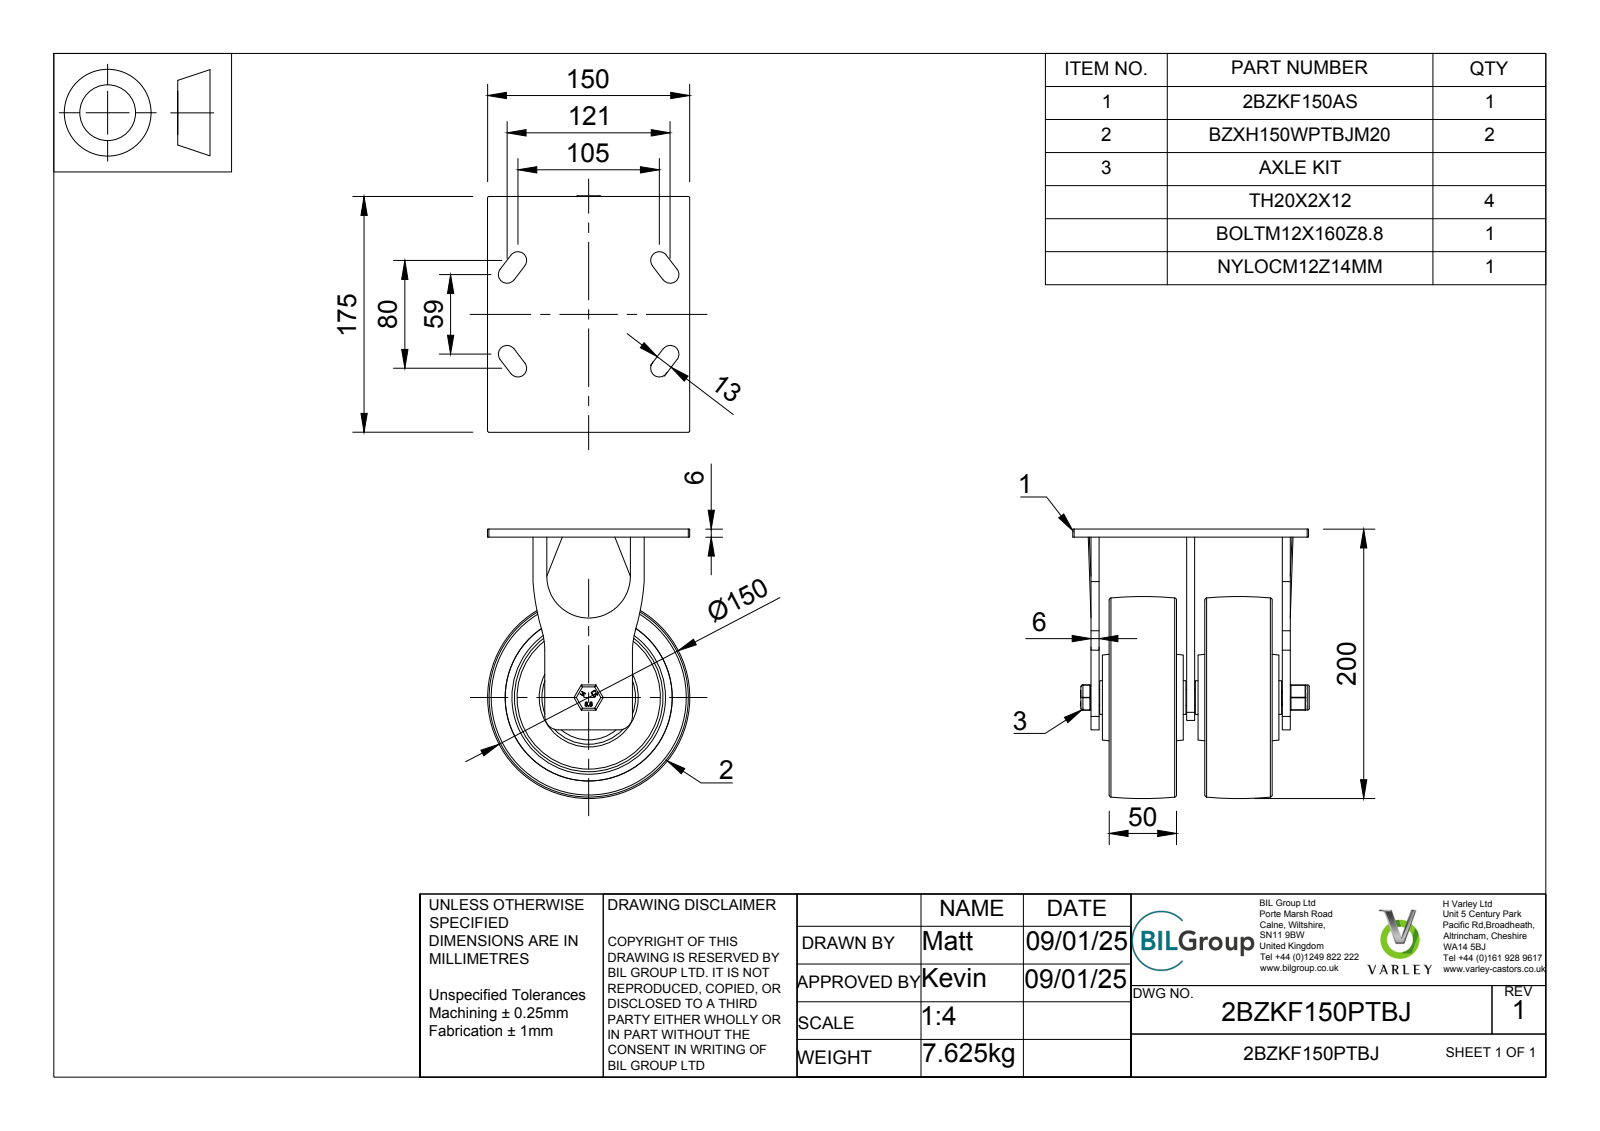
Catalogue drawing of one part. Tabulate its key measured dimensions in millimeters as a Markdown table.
| quantity | value |
| --- | --- |
| part name | 2BZKF150PTBJ v3; 2BZKF150AS v1; 2BZKF150AS; STEEL FABRICATED BRACKET (+8 more) |
| STEP written by | Autodesk Translation Framework v13.20.0.188 (AP242_MANAGED_MODEL_BASED_3D_ENGINEERING_MIM_LF) |
| units | millimeters |
| bodies | 66 solids, 2298 faces (1050 planar, 450 cylindrical, 798 other) |
| overall size | 200 × 175.5 × 150 |
| volume | 1 490 000 mm³ |
| surface area | 462 744 mm² |
| round holes (diameter × count) | 12 × 1, 12.2 × 1, 13 × 1, 14 × 1, 20 × 1, 28.5 × 1, 41.5 × 1, 42 × 1, 44 × 1, 47 × 1, 124 × 1 |
| round bosses / shafts (diameter × count) | 40.5 × 1, 40 × 1, 29 × 1, 27 × 1, 25 × 1, 24 × 1, 19.8 × 1, 18.5 × 1 |
| partial cylindrical surfaces (radius × count) | 6 × 26, 4 × 24, 0.5 × 18, 0.25 × 12, 6.5 × 8, 1.5 × 6, 0.47 × 4, 0.9 × 4 |
| main face-to-face distances | 71, 6, 35.5, 7.5, 57.5, 13.5, 63.5, 41.5, 106.5, 29.5 |
